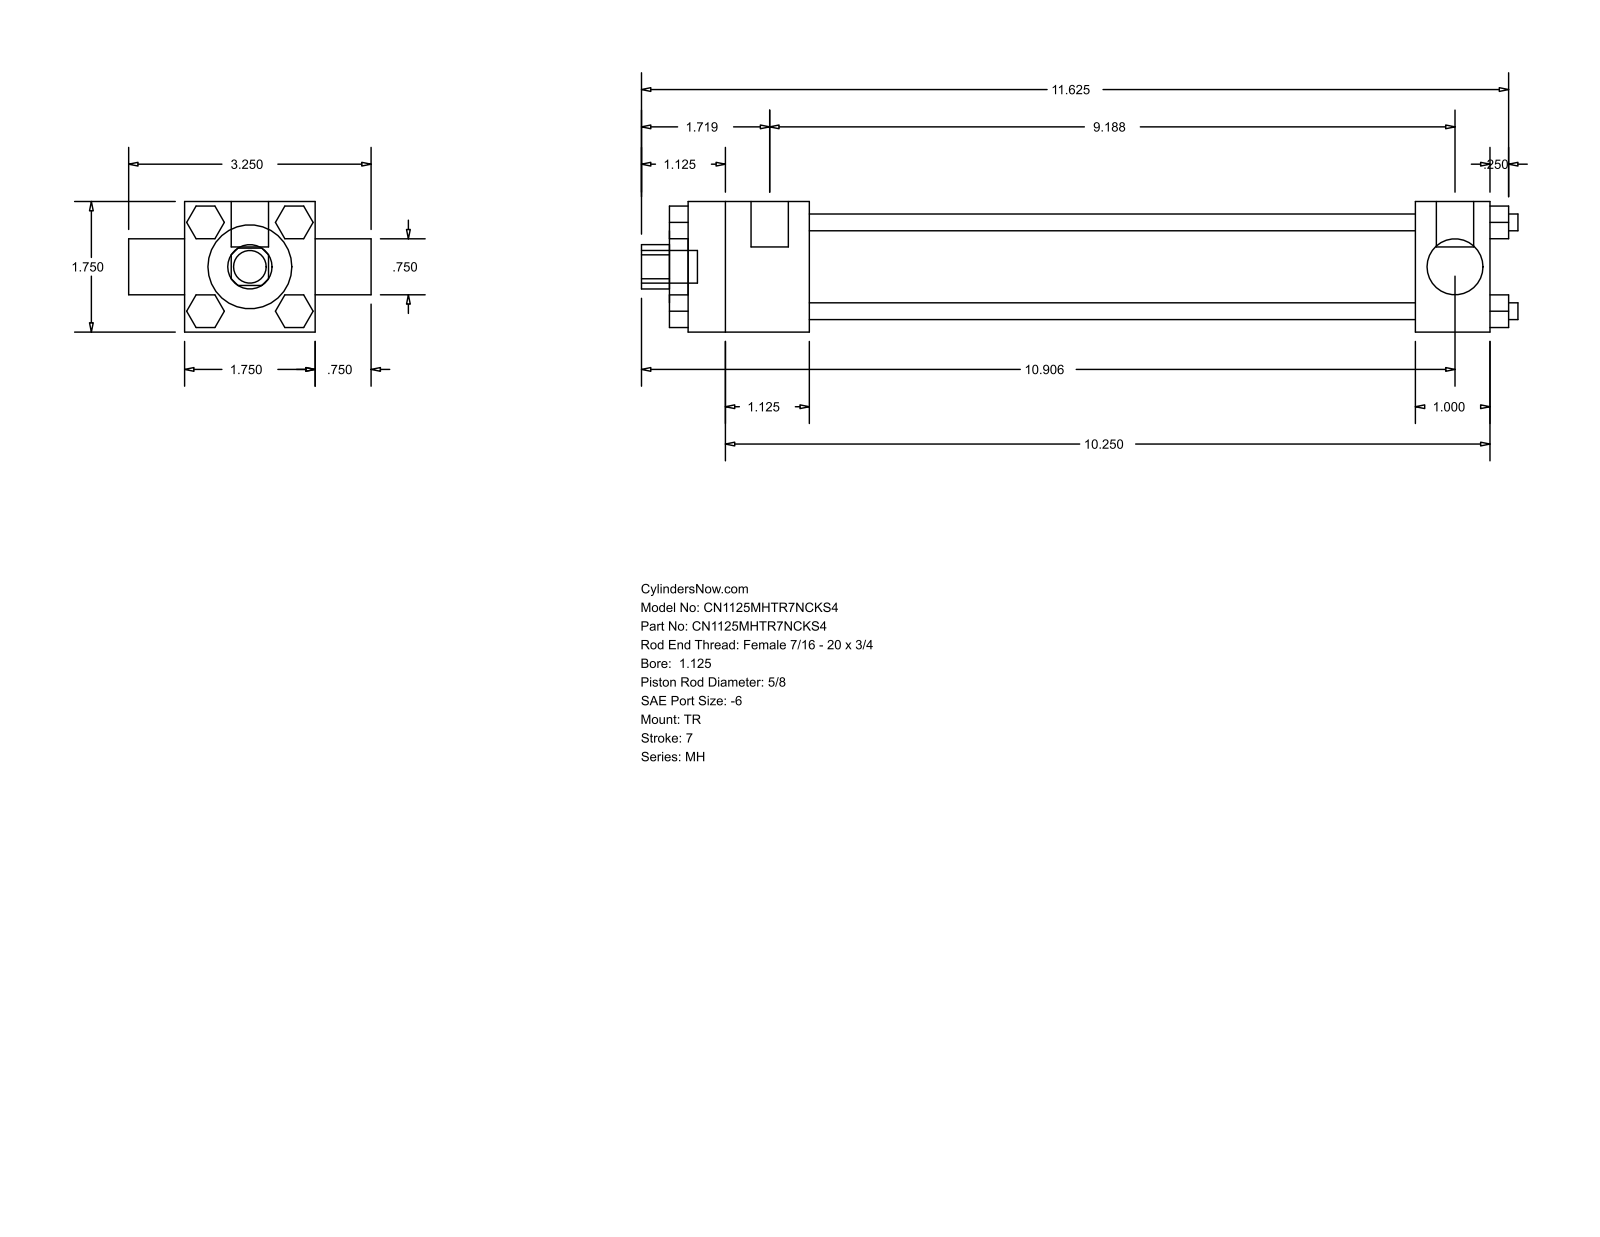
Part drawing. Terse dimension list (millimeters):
name: MH_TR__0112_0.625
written by: GSSL Pune (CONFIG_CONTROL_DESIGN)
unit: mm
bodies: 0 solids, 120 faces (92 planar, 28 cylindrical, 0 other)
size: 298.45 × 82.55 × 44.45
holes: 1× ⌀15.88, 1× ⌀19.05, 1× ⌀28.57, 1× ⌀34.92
bosses: 4× ⌀5.71, 3× ⌀5.56, 2× ⌀12.7, 1× ⌀11.11
rounds: 1× R7.54
face distances: 44.46, 11.11, 206.37, 231.78, 25.41, 41.27, 247.64, 273.05, 47.62, 279.4
